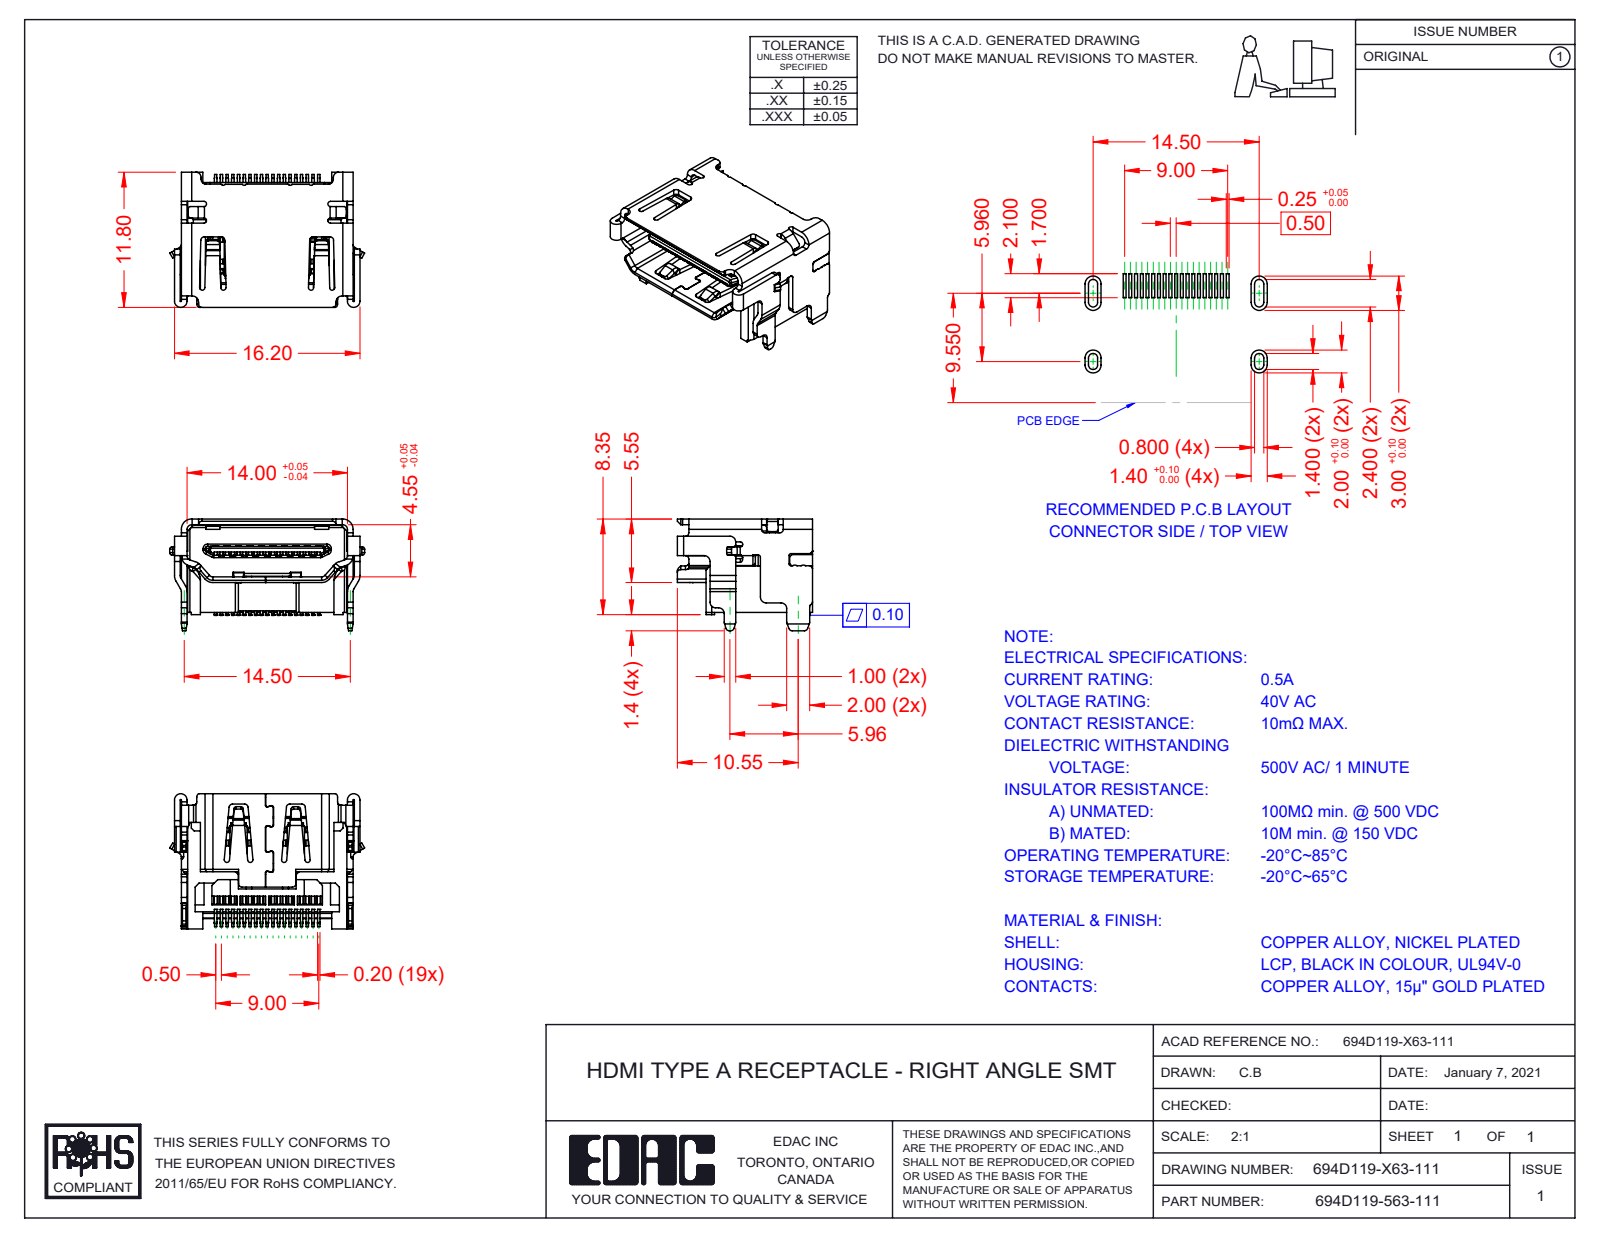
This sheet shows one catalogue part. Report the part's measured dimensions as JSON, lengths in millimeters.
{"part_name": "Insulator 694D119-X63-111; Contacts 694D119-X63-111; Shell 694D119-X63-111; 694D119-163-111", "step_written_by": "SolidWorks 2020 (AUTOMOTIVE_DESIGN)", "units": "millimeters", "bodies": {"solids": 21, "faces": 3479, "planar": 2261, "cylindrical": 1100, "other": 118}, "overall_size": [17.02, 11.8, 9.75], "volume_mm3": 549, "surface_area_mm2": 2210, "partial_cylinders_radius": [[0.2, 200], [0.15, 96], [0.1, 47], [0.3, 38], [0.11, 20], [0.5, 15], [0.23, 13], [1, 10]], "face_to_face_distances": [0.5, 5.05, 0.55, 0.7, 14.5, 14.45, 13.95, 2.52, 2.53, 2.67]}
